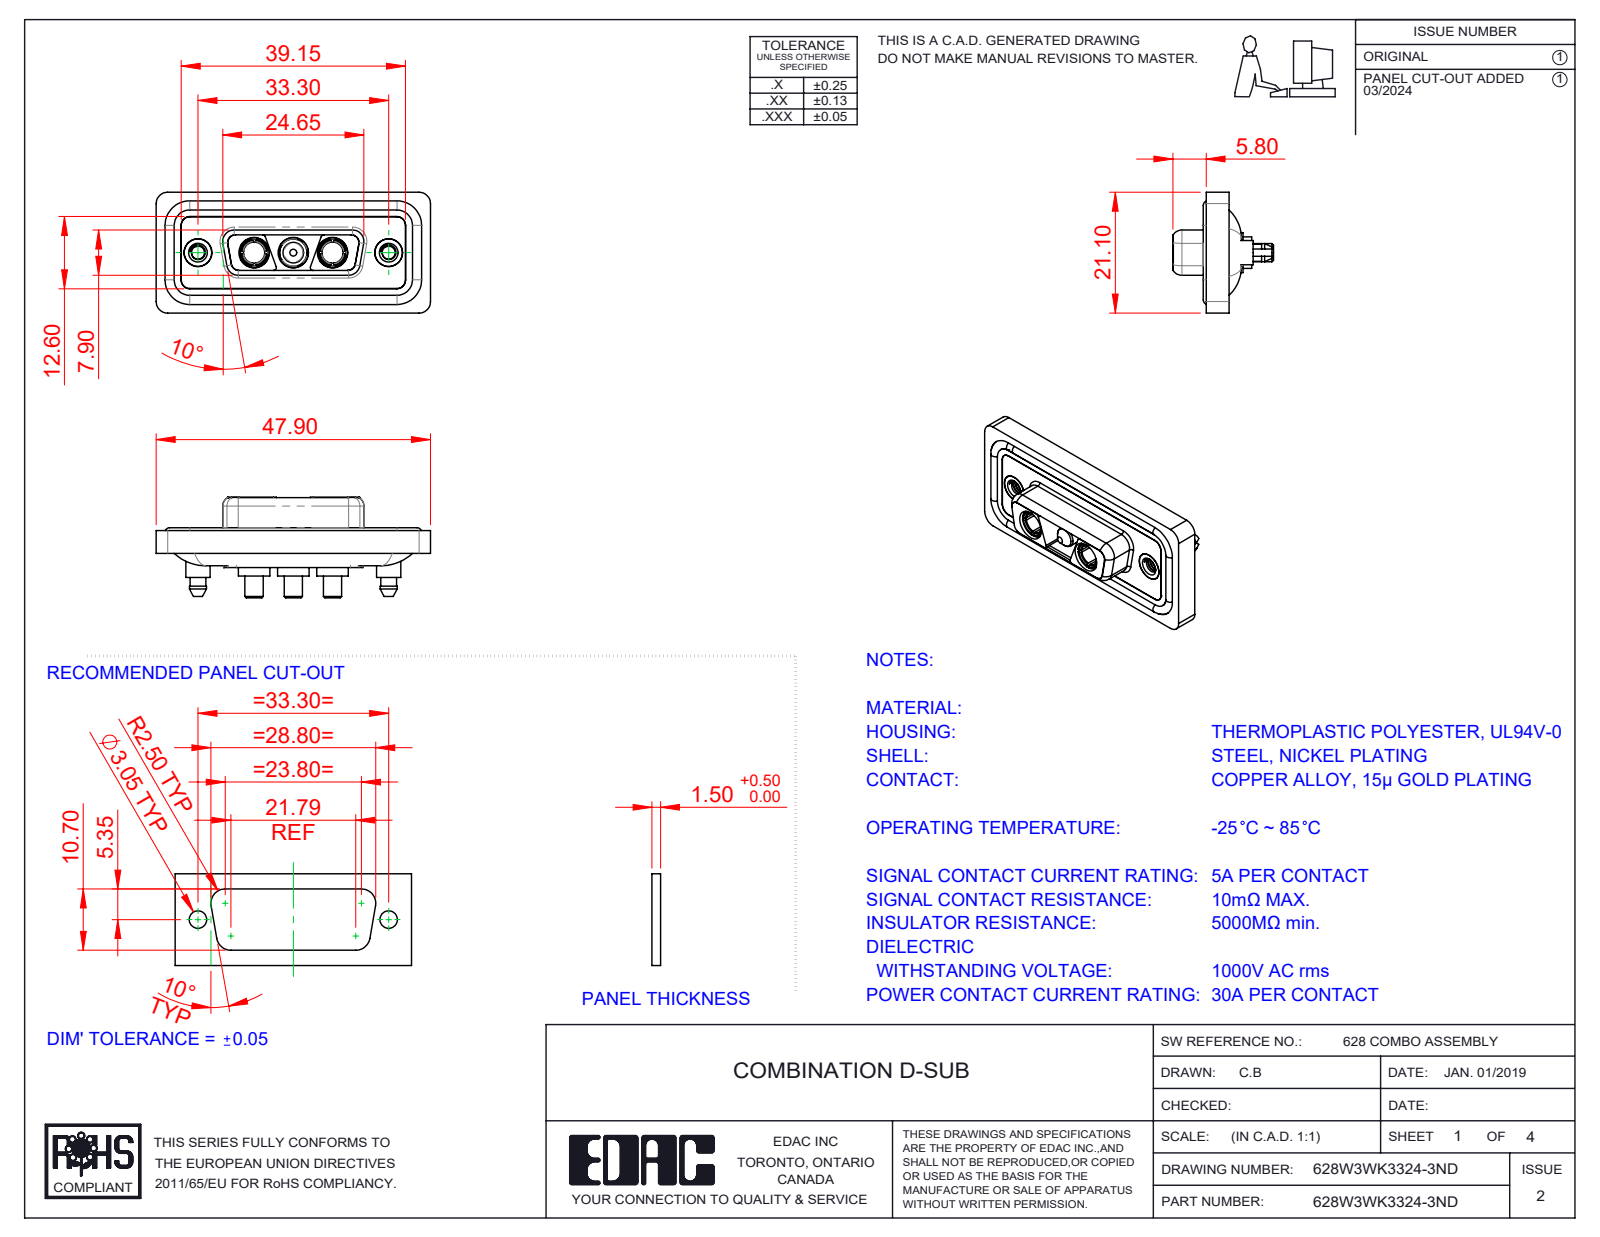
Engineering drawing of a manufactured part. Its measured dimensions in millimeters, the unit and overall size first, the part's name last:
Units: millimetres
Overall size (bounding box): 47.9 × 21.1 × 17.55
Round holes (diameter × count): ⌀4.85 ×5, ⌀5.3 ×3, ⌀2.26 ×2, ⌀3.7 ×2, ⌀4 ×2, ⌀4.05 ×2, ⌀5 ×2
Round bosses / shafts (diameter × count): ⌀1.6 ×4, ⌀5.5 ×3, ⌀5.2 ×3, ⌀4.75 ×3, ⌀3.75 ×3, ⌀3.2 ×3, ⌀5.4 ×2, ⌀4.96 ×2
Partial cylindrical surfaces — rounded edges, fillets, slot ends (radius × count): R1.5 ×24, R2 ×20, R1.35 ×12, R1.6 ×10, R0.5 ×8, R0.25 ×4, R0.6 ×4, R0.65 ×4
Main face-to-face distances: 0.4, 1.6, 1.8, 0.5, 1.1, 2.9, 5.65, 7.05, 1.5, 5.35
Hole centre spacings: 6.85, 9.8, 16.65, 23.5, 13.7, 33.3
Volume: 6 035 mm³ · Surface area: 9 858 mm²
Bodies: 13 solids, 649 faces (194 planar, 306 cylindrical, 149 other)
Part name (STEP PRODUCT): 628Combo Shell Rear_15 Contacts; Power Socket_30A S; 628Combo Shell Front_15 Contacts; 628W3WK3324-3ND (+4 more)
STEP written by: SolidWorks 2023 (CONFIG_CONTROL_DESIGN)
